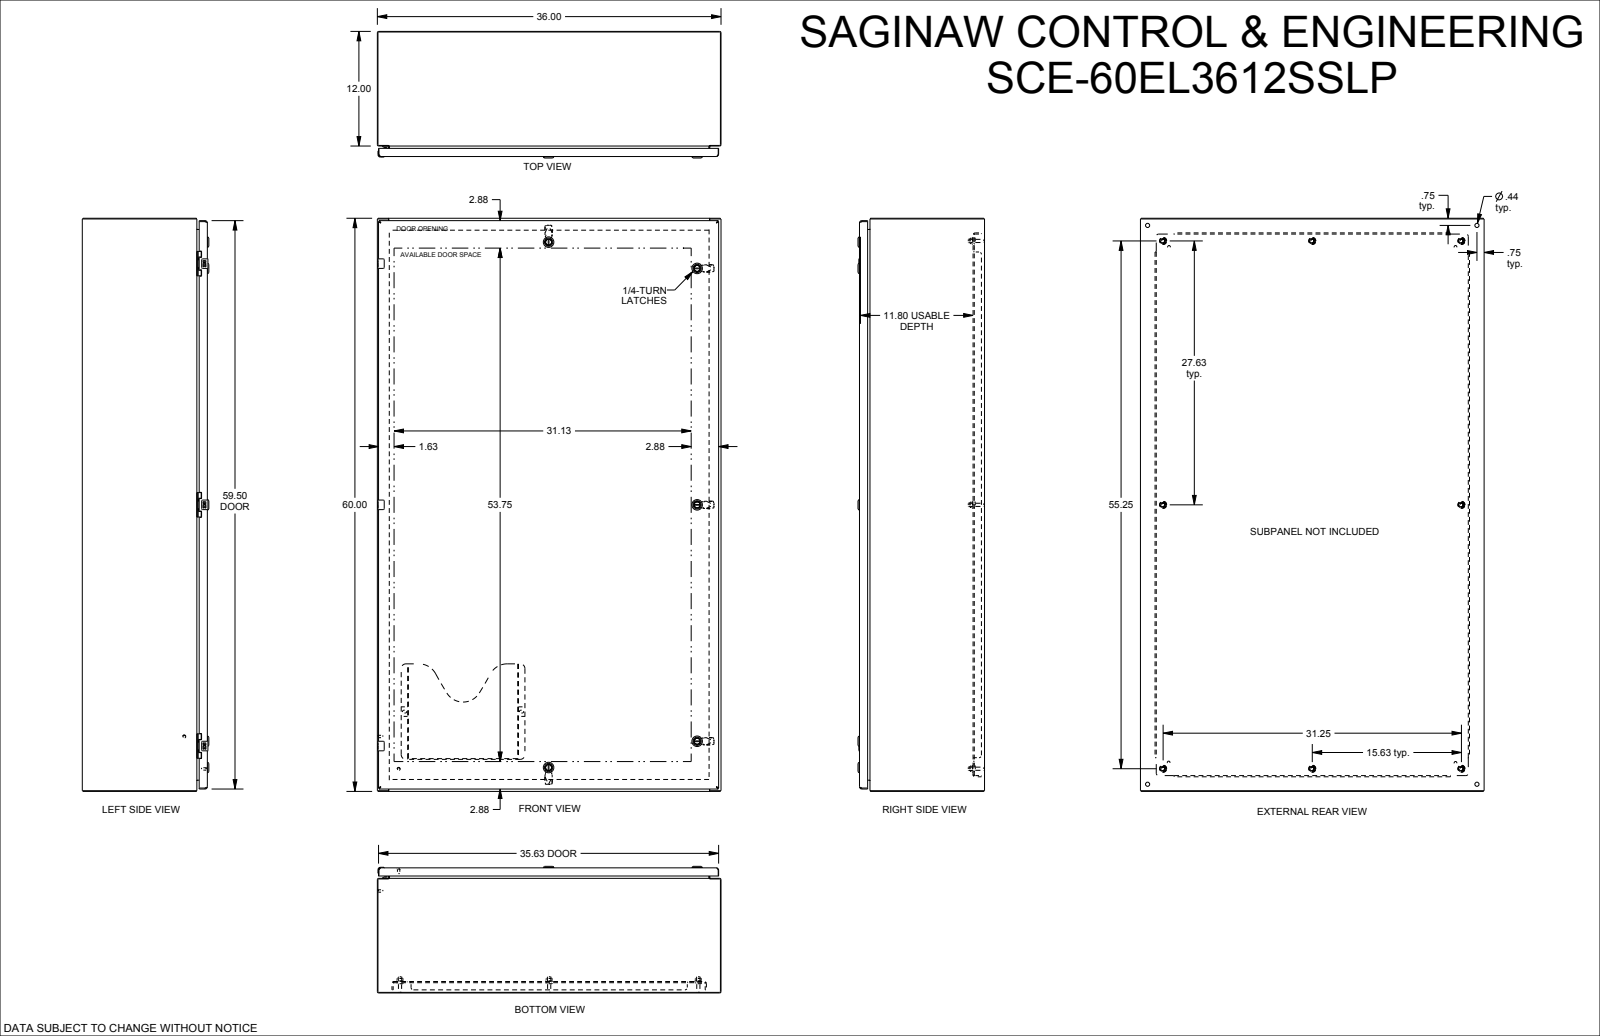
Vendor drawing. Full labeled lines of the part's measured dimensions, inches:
Part name (STEP PRODUCT): SCE-60EL3612LP
STEP written by: SolidWorks 2021 (AUTOMOTIVE_DESIGN)
Units: inches
Bodies: 42 solids, 2312 faces (1156 planar, 773 cylindrical, 383 other)
Overall size (bounding box): 60 × 36 × 13.967
Volume: 806 in³ · Surface area: 19 008 in²
Round holes (diameter × count): ⌀0.5 ×8, ⌀0.172 ×6, ⌀0.205 ×6, ⌀0.244 ×6, ⌀0.375 ×6, ⌀0.197 ×5, ⌀0.394 ×5, ⌀0.634 ×5, ⌀0.281 ×4, ⌀0.437 ×4, ⌀0.04 ×3, ⌀0.218 ×3
Round bosses / shafts (diameter × count): ⌀0.17 ×9, ⌀0.375 ×8, ⌀0.33 ×8, ⌀0.25 ×6, ⌀0.24 ×6, ⌀1.102 ×5, ⌀0.78 ×5, ⌀0.63 ×5
Partial cylindrical surfaces — rounded edges, fillets, slot ends (radius × count): R0.015 ×28, R0.157 ×20, R0.04 ×17, R0.26 ×16, R0.031 ×14, R0.03 ×12, R0.043 ×12, R0.062 ×12
Main face-to-face distances: 0.075, 0.06, 13.097, 13.022, 13.037, 12.962, 1.125, 0.125, 1.075, 1
Hole centre spacings: 25.25, 17.327, 2.298, 15.625, 27.625, 29.296, 31.738, 32.916
